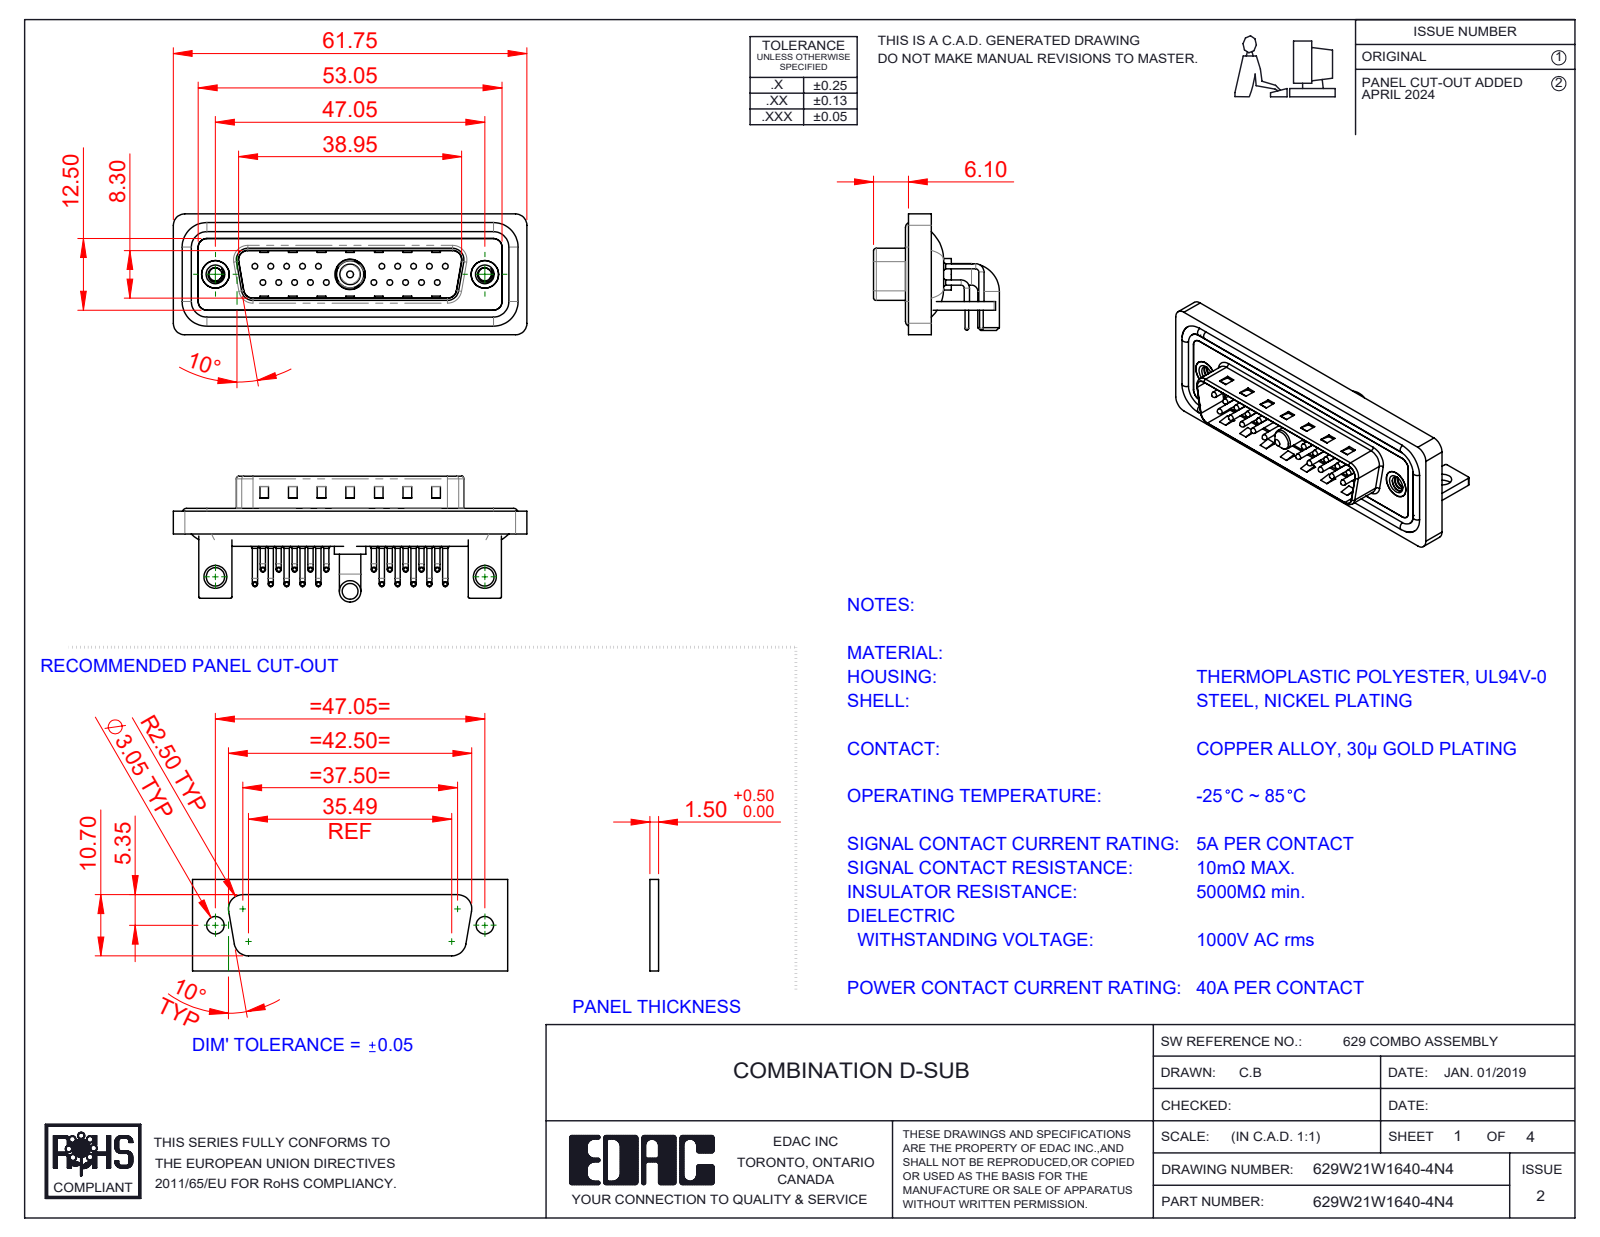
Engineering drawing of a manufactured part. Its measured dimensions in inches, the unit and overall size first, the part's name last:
Units: inches
Overall size (bounding box): 2.431 × 0.865 × 0.831
Round holes (diameter × count): ⌀0.03 ×20, ⌀0.063 ×20, ⌀0.079 ×20, ⌀0.089 ×2, ⌀0.126 ×2, ⌀0.157 ×2, ⌀0.189 ×2, ⌀0.197 ×2, ⌀0.191 ×1, ⌀0.209 ×1
Round bosses / shafts (diameter × count): ⌀0.035 ×40, ⌀0.059 ×20, ⌀0.039 ×20, ⌀0.026 ×20, ⌀0.063 ×4, ⌀0.193 ×2, ⌀0.148 ×2, ⌀0.217 ×1
Partial cylindrical surfaces — rounded edges, fillets, slot ends (radius × count): R0.04 ×20, R0.079 ×19, R0.059 ×18, R0.01 ×16, R0.02 ×9, R0.063 ×8, R0.024 ×4, R0.026 ×4
Main face-to-face distances: 0.016, 0.031, 0.083, 0.114, 0.059, 0.043, 0.161, 0.063, 0.177, 0.146
Hole centre spacings: 0.124, 0.109, 0.218, 0.327, 0.198, 0.763, 0.826, 0.872
Volume: 0.474 in³ · Surface area: 20.7 in²
Bodies: 31 solids, 2766 faces (1519 planar, 947 cylindrical, 300 other)
Part name (STEP PRODUCT): 629W21W1640-4N4; 629Combo Housing_21W1; 629Combo Contact Row 1; 629Combo Waterproof Housing_25 Contacts (+6 more)
STEP written by: SolidWorks 2023 (CONFIG_CONTROL_DESIGN)
